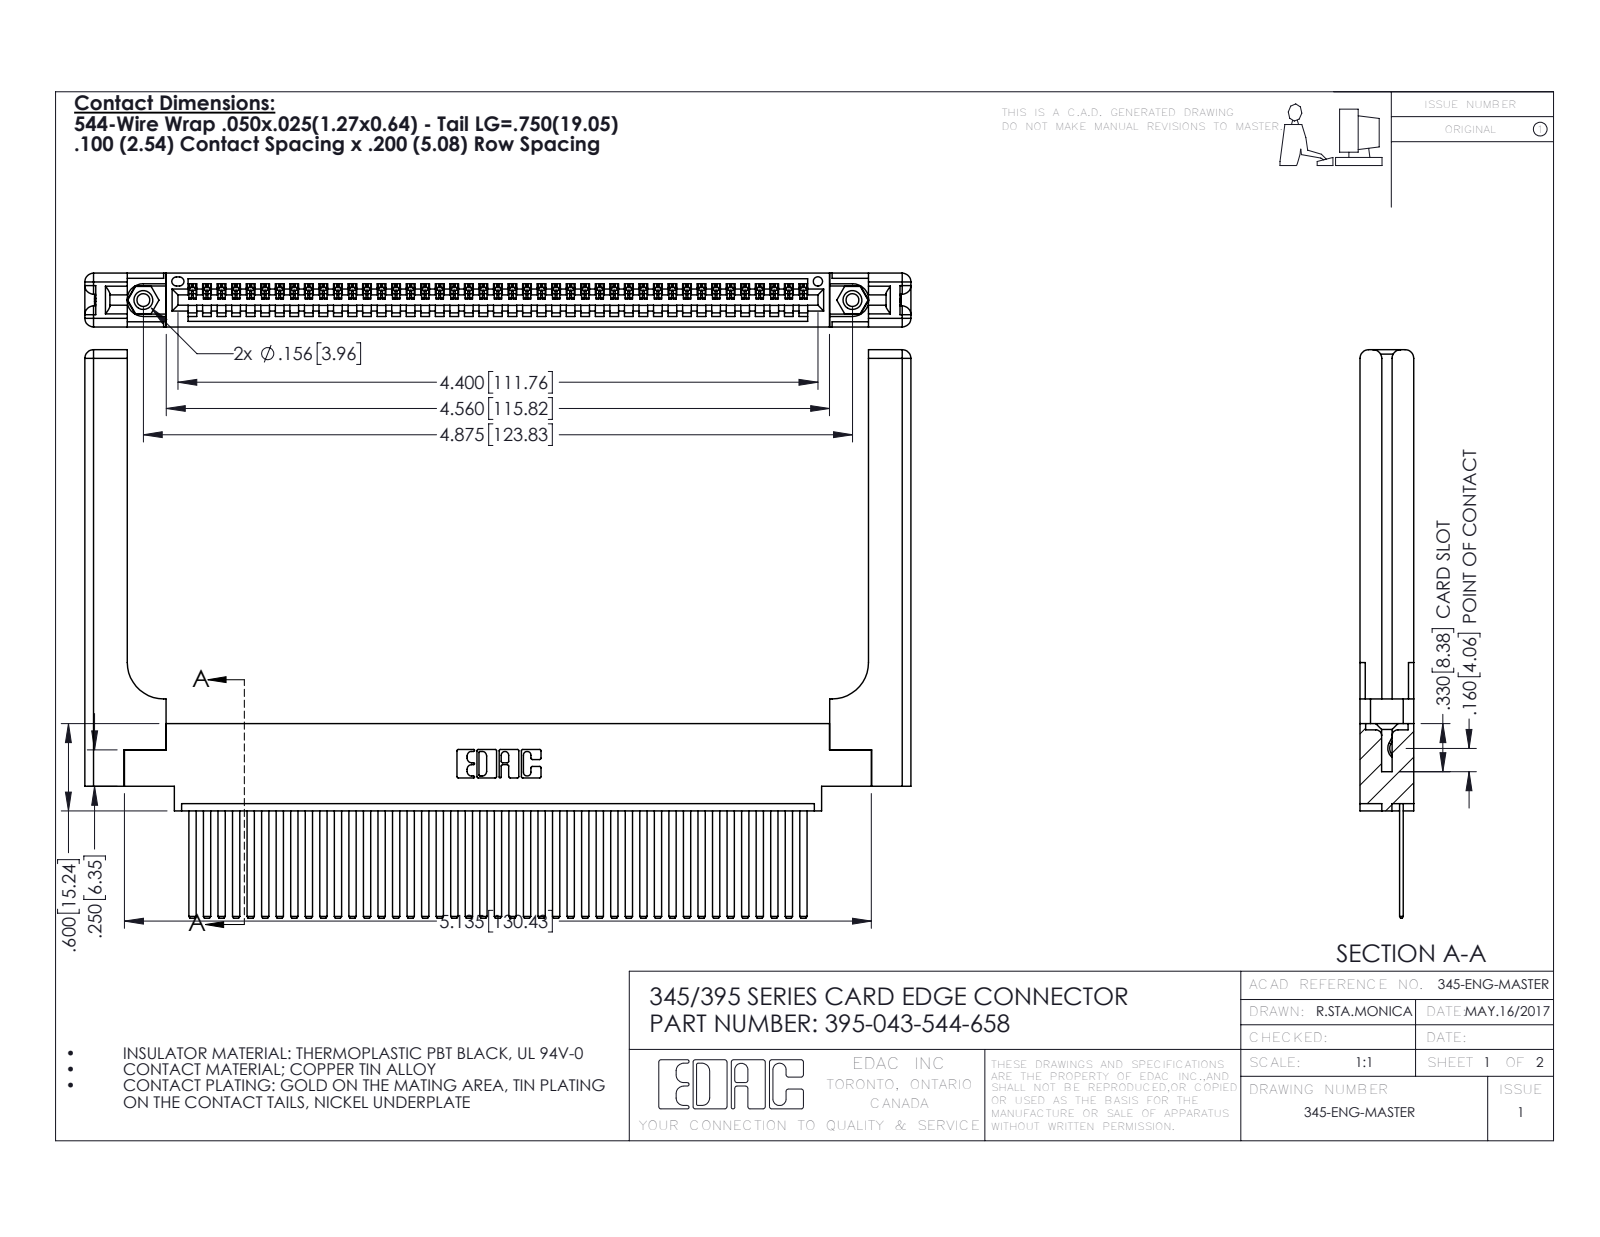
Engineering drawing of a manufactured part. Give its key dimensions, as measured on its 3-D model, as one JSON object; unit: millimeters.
{"part_name": "345-220-058_345-220-058; 345-250-001_345-250-001-102; 345 Part_0.170 Offset - 0.156 Dia-TH; 395-043-544-658 (+1 more)", "step_written_by": "SolidWorks 2016 (CONFIG_CONTROL_DESIGN)", "units": "millimeters", "bodies": {"solids": 48, "faces": 2622, "planar": 1780, "cylindrical": 782, "other": 60}, "overall_size": [144.2, 99.2, 9.4], "volume_mm3": 22600, "surface_area_mm2": 25670, "round_holes": [[2.3, 2], [3.2, 2], [4, 2], [1.6, 1]], "round_bosses_or_shafts": [[3.9, 2]], "partial_cylinders_radius": [[0.2, 86], [0.3, 22], [1.5, 16], [0.2, 6], [0.8, 6], [0.7, 3], [0.8, 2], [0.8, 2]], "face_to_face_distances": [1.8, 7.6, 9.4, 2.5, 6.9, 0.6, 5.1, 5.7, 3.8, 3.8], "hole_center_spacings": [6.9, 117.8, 123.8]}
